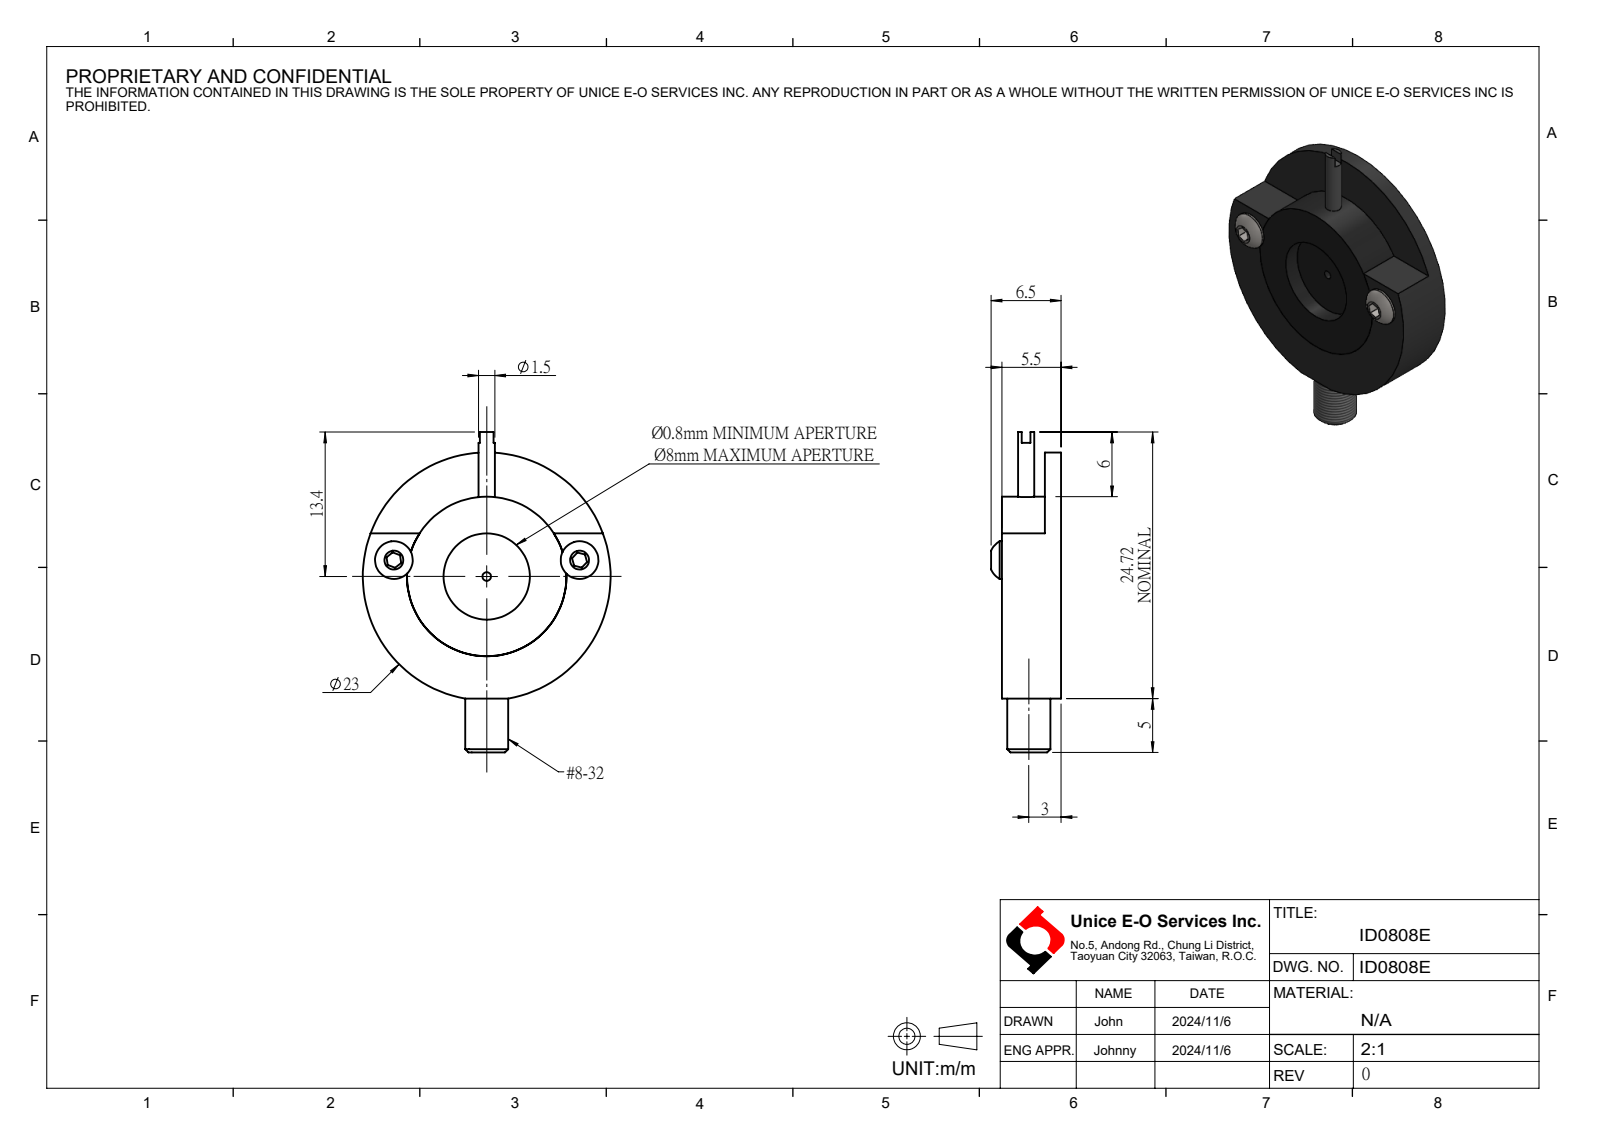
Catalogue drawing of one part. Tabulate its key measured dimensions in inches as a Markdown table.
| quantity | value |
| --- | --- |
| part name | ID0808E |
| STEP written by | SolidWorks 2024 (AUTOMOTIVE_DESIGN) |
| units | inches |
| bodies | 0 solids, 61 faces (32 planar, 23 cylindrical, 6 other) |
| overall size | 1.17 × 0.906 × 0.256 |
| round holes (diameter × count) | 0.031 × 1, 0.315 × 1, 0.465 × 1, 0.583 × 1 |
| round bosses / shafts (diameter × count) | 0.138 × 2, 0.906 × 1, 0.157 × 1, 0.059 × 1 |
| main face-to-face distances | 0.217, 0.059, 0.039, 0.157, 0.177, 0.098, 0.118, 0.02, 0.603, 0.197 |
